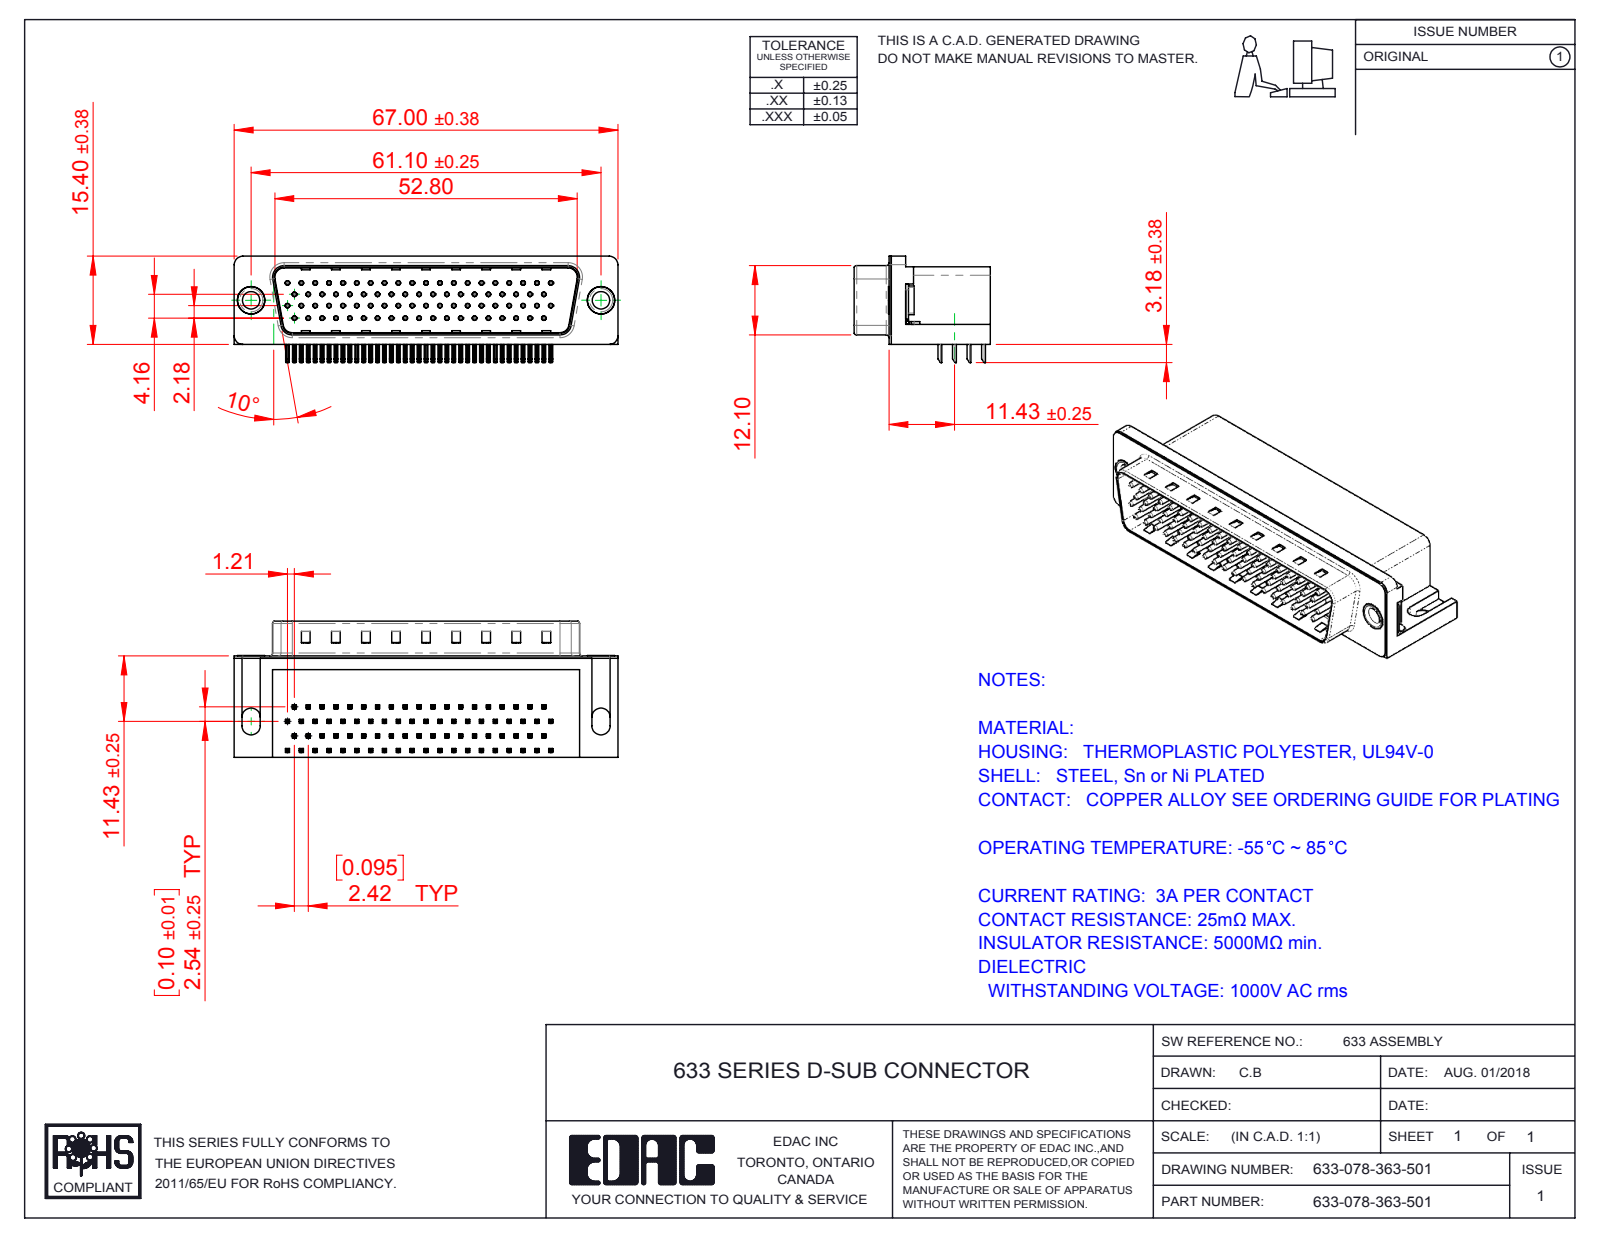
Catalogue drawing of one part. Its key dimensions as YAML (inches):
part_name: "633 Non Board Mount_78 Contact; 633 Shell_78 Contact; 633 Contact Bottom_78 Contact; 633 Contact Top 78 (+5 more)"
step_written_by: "SolidWorks 2016 (CONFIG_CONTROL_DESIGN)"
units: inches
bodies: {solids: 84, faces: 6230, planar: 3979, cylindrical: 1756, other: 495}
overall_size: [2.638, 0.937, 0.731]
volume: 0.888
surface_area: 24.96
round_holes:
  - {diameter: 0.014, count: 78}
  - {diameter: 0.031, count: 78}
  - {diameter: 0.12, count: 2}
  - {diameter: 0.157, count: 2}
  - {diameter: 0.189, count: 2}
  - {diameter: 0.197, count: 2}
round_bosses_or_shafts:
  - {diameter: 0.03, count: 78}
  - {diameter: 0.193, count: 2}
  - {diameter: 0.187, count: 2}
  - {diameter: 0.152, count: 2}
partial_cylinders:
  - {radius: 0.01, count: 320}
  - {radius: 0.005, count: 156}
  - {radius: 0.039, count: 16}
  - {radius: 0.02, count: 9}
  - {radius: 0.063, count: 8}
  - {radius: 0.059, count: 6}
  - {radius: 0.018, count: 4}
  - {radius: 0.035, count: 4}
face_to_face_distances: [0.016, 0.52, 0.681, 0.461, 0.526, 0.081, 0.541, 0.065, 0.469, 0.073]
hole_center_spacings: [0.095, 0.191, 0.286, 0.381, 0.246, 0.281, 0.476, 0.339]
